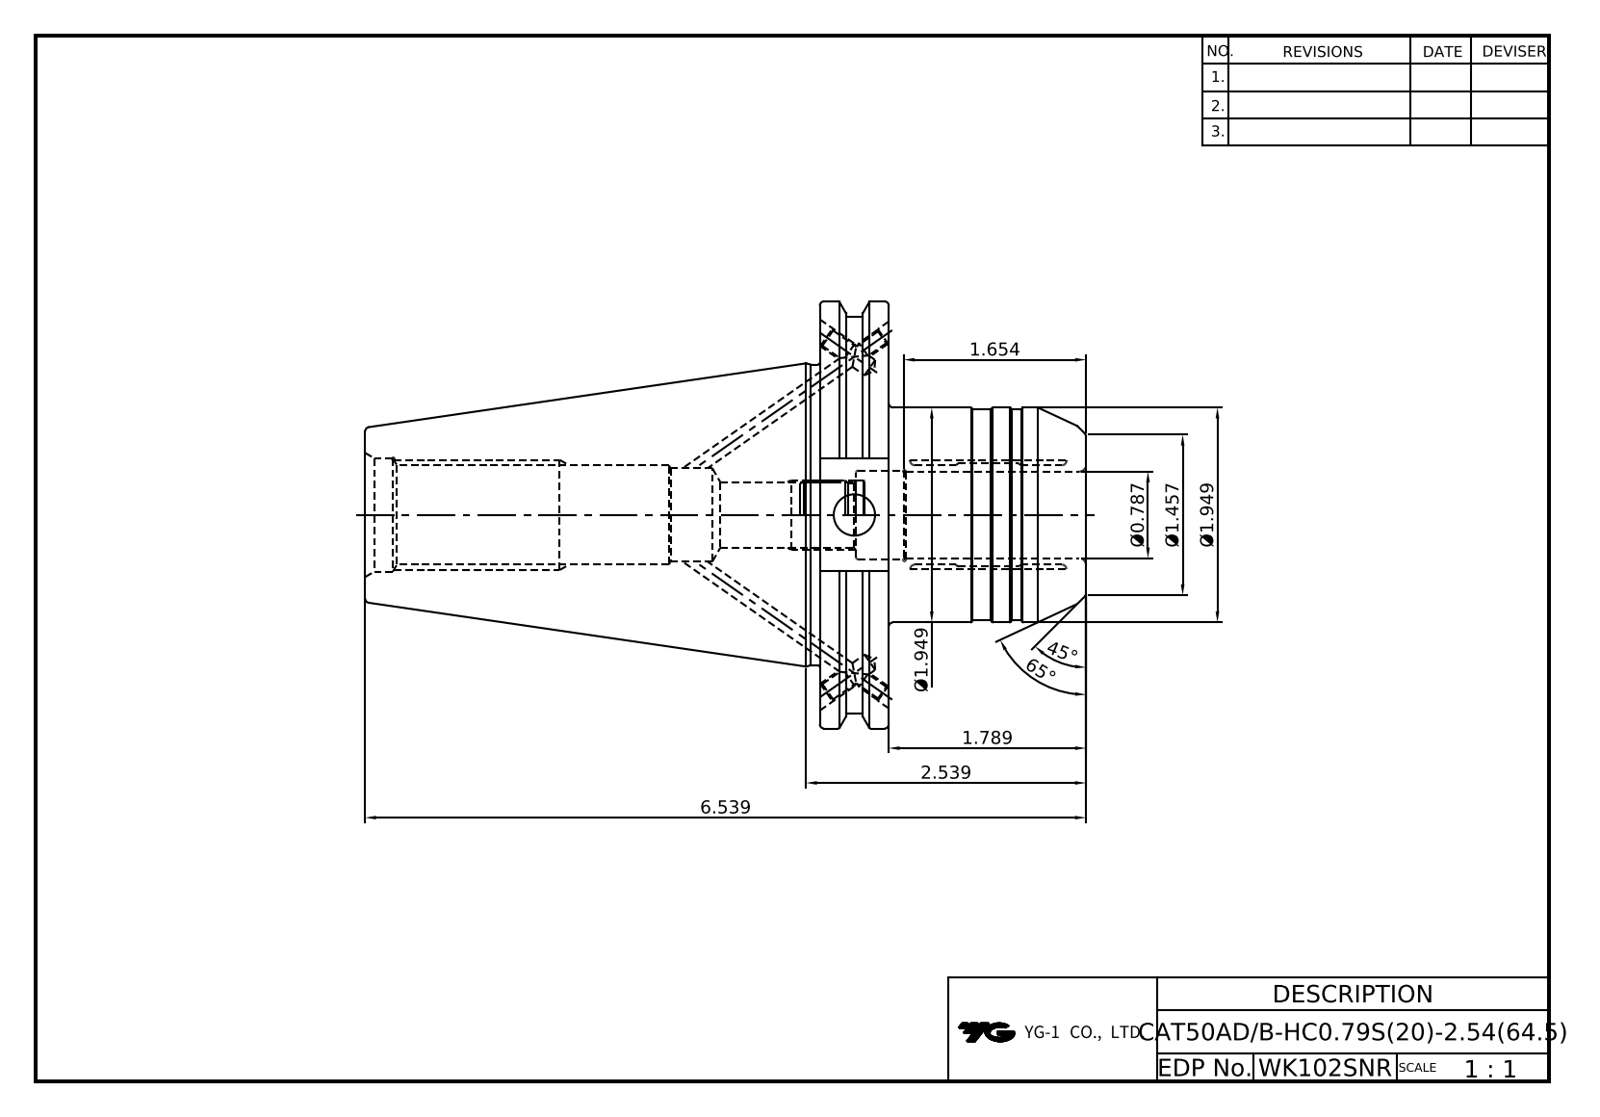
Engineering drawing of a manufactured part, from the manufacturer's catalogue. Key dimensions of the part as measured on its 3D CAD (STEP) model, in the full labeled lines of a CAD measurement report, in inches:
Part name (STEP PRODUCT): LO-CAT50ADB-HC20S-64
STEP written by: Autodesk Inventor 2020 (AUTOMOTIVE_DESIGN)
Units: inches
Bodies: 1 solid, 101 faces (32 planar, 31 cylindrical, 38 other)
Overall size (bounding box): 6.539 × 3.875 × 3.728
Volume: 23.95 in³ · Surface area: 83.78 in²
Round holes (diameter × count): ⌀0.163 ×4, ⌀0.197 ×4, ⌀0.375 ×1, ⌀0.587 ×1, ⌀0.787 ×1, ⌀0.803 ×1, ⌀0.846 ×1, ⌀0.865 ×1, ⌀1.031 ×1
Round bosses / shafts (diameter × count): ⌀3.875 ×1, ⌀3.594 ×1, ⌀2.726 ×1, ⌀1.949 ×1, ⌀1.909 ×1
Main face-to-face distances: 0.625, 2.415, 1.789, 4.125, 4.75, 6.539, 2.875, 1.02, 4.514, 0.389
Hole centre spacings: 2.35
